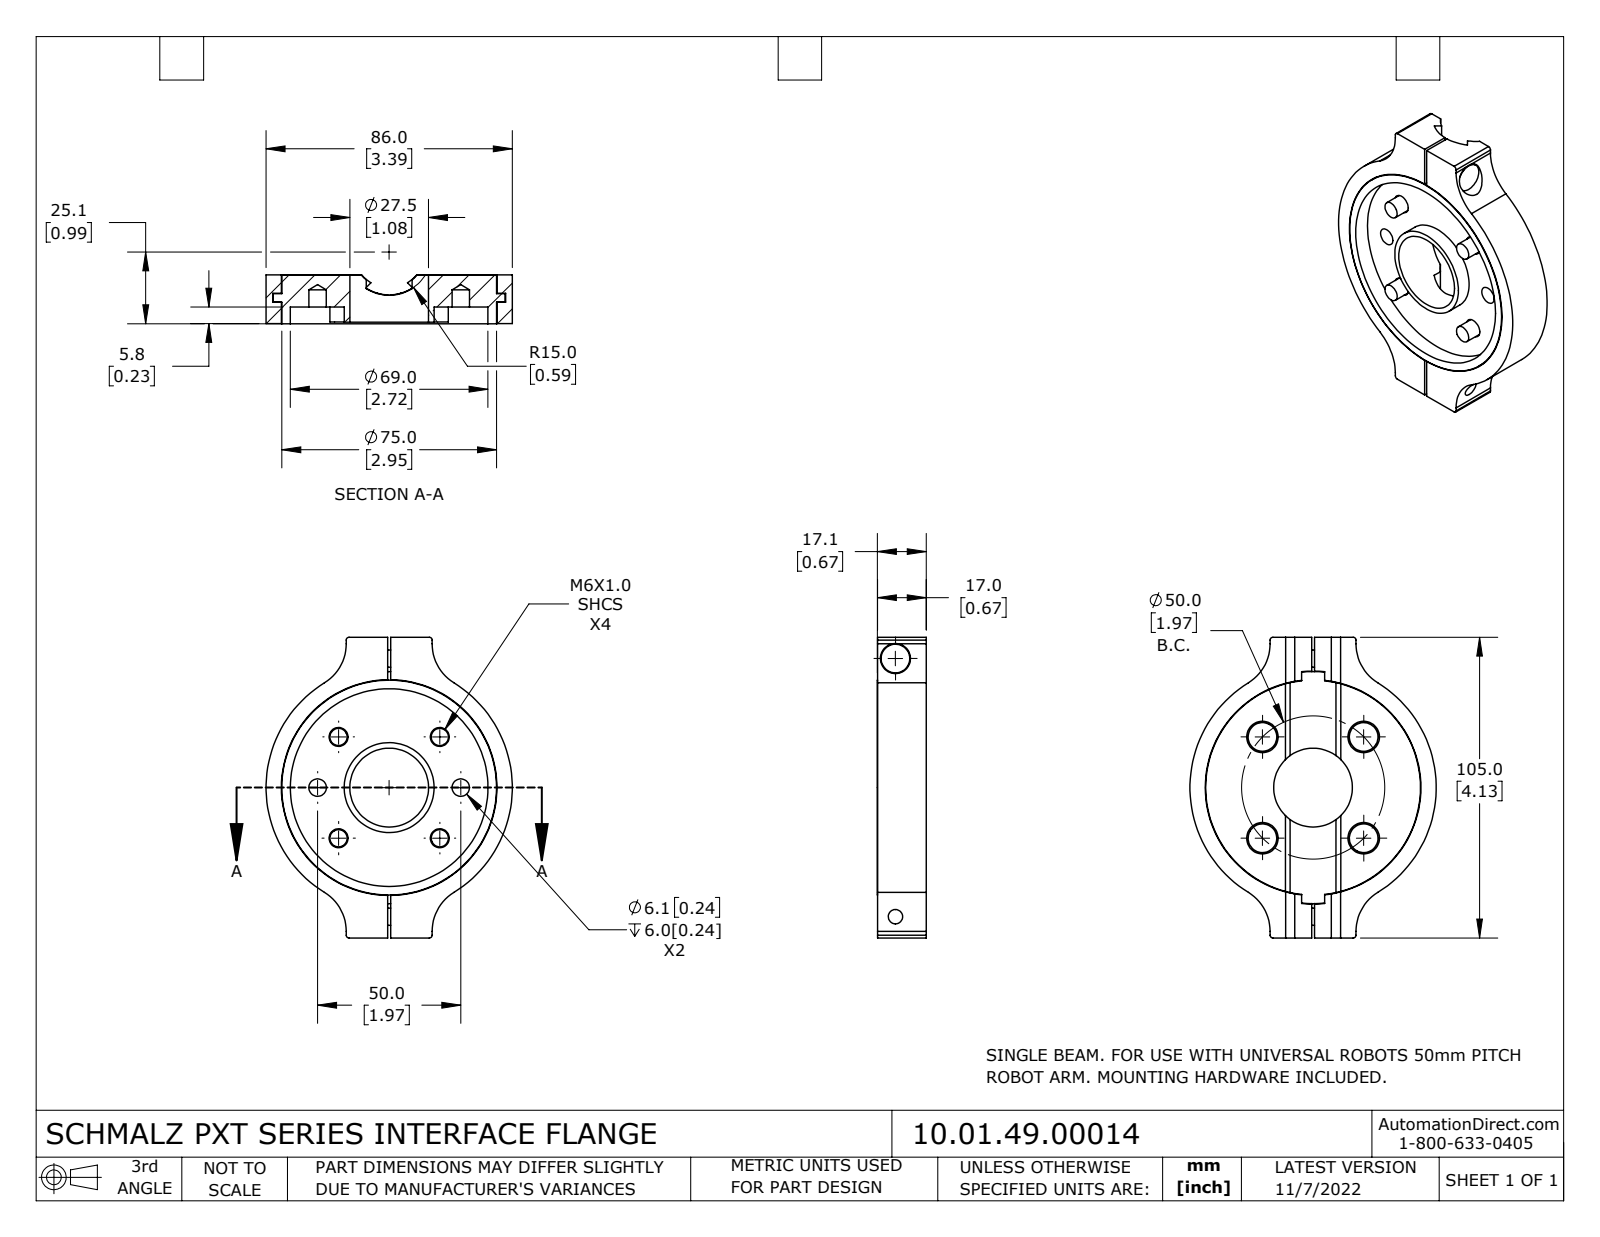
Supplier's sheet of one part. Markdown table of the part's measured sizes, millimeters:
| quantity | value |
| --- | --- |
| part name | 10.01.49.00014 |
| STEP written by | SolidWorks 2021 (CONFIG_CONTROL_DESIGN) |
| units | millimeters |
| bodies | 9 solids, 167 faces (60 planar, 103 cylindrical, 4 other) |
| overall size | 105 × 86 × 17.05 |
| volume | 73 232 mm³ |
| surface area | 37 508 mm² |
| round holes (diameter × count) | 6.6 × 4, 11 × 4, 5 × 2, 6.1 × 2, 6.3 × 2, 10.5 × 2, 27.5 × 1, 69 × 1, 75.3 × 1, 81.3 × 1 |
| round bosses / shafts (diameter × count) | 10 × 6, 6 × 6, 81 × 1, 75 × 1, 31.4 × 1 |
| partial cylindrical surfaces (radius × count) | 1 × 4, 16 × 4, 12.5 × 1, 12.55 × 1, 15 × 1, 15.05 × 1, 43 × 1 |
| main face-to-face distances | 11.2, 17, 16.95, 5.75, 9.5, 1.7, 7.45, 9.55, 11.25, 6.45 |
| hole center spacings | 25, 19.14, 35.36, 46.2, 50.01, 50, 90.1 |
